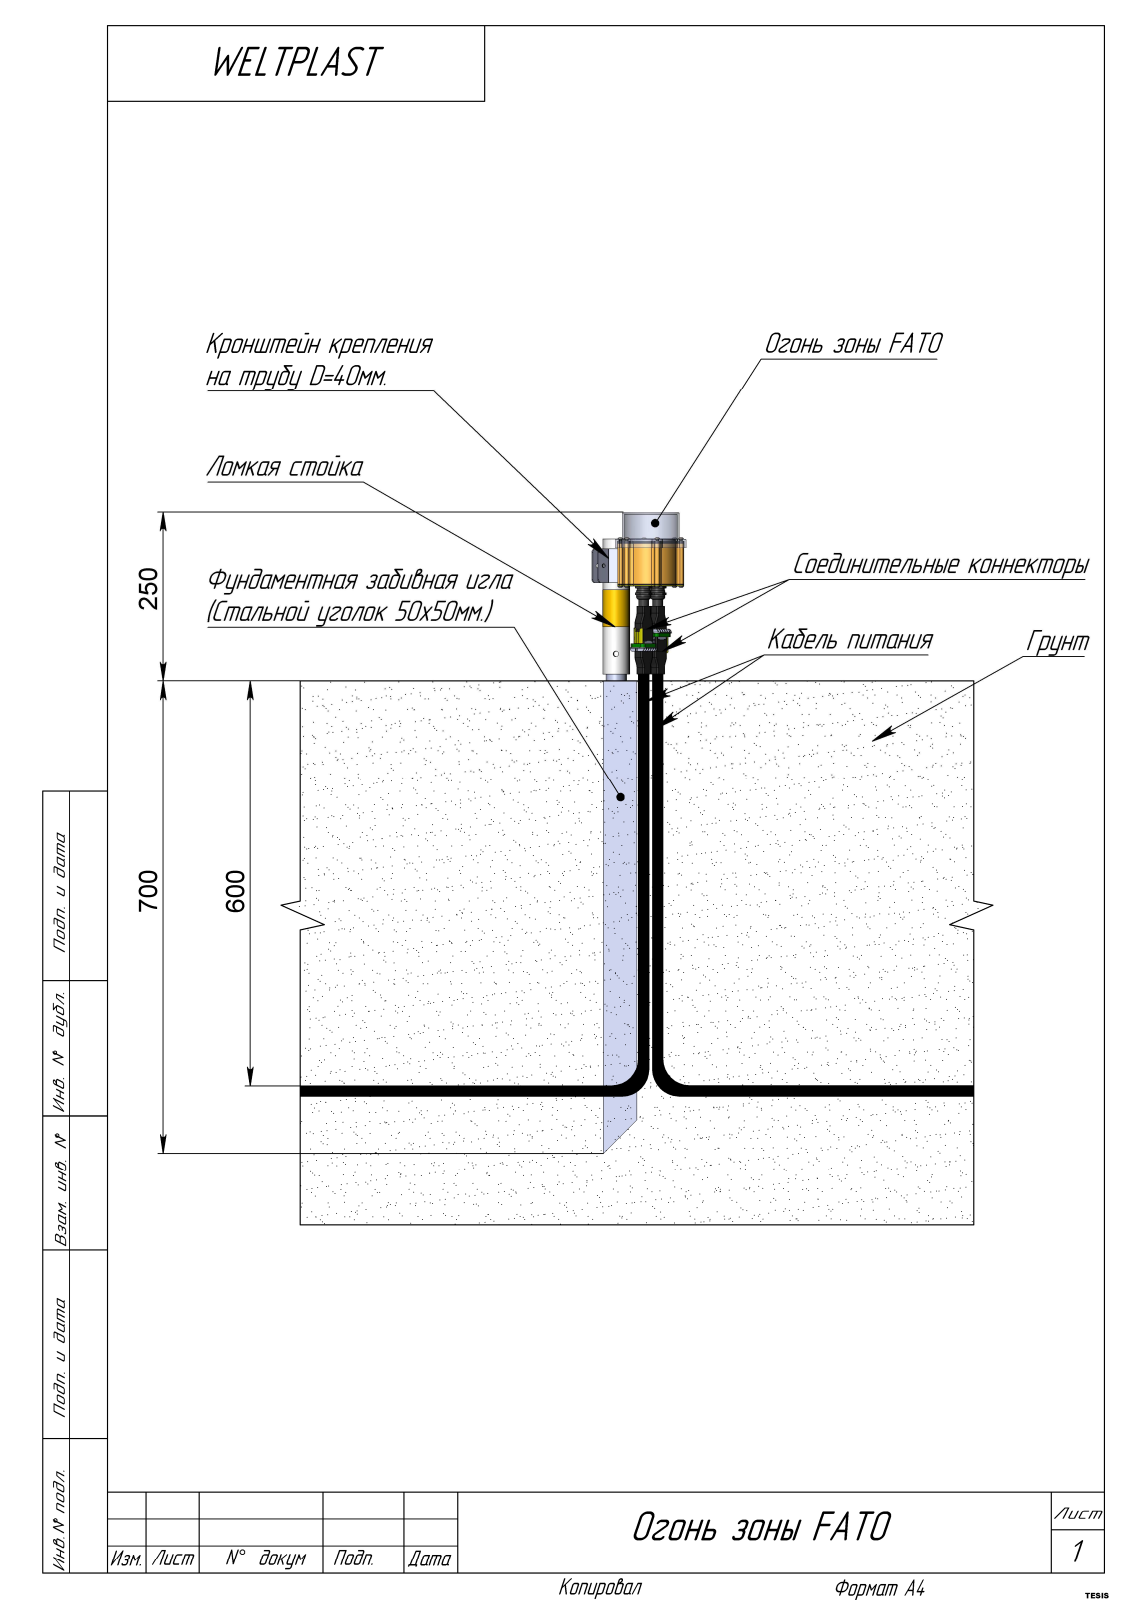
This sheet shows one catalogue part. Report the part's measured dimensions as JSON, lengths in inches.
{"part_name": "Конектор мама Сборка 1; Втулка; LLC-AB-60; гайка под провода (+8 more)", "step_written_by": "SolidWorks 2017 (AUTOMOTIVE_DESIGN)", "units": "inches", "bodies": {"solids": 44, "faces": 3008, "planar": 885, "cylindrical": 1069, "other": 1054}, "overall_size": [37.402, 5.663, 5.512], "volume_in3": 43.83, "surface_area_in2": 655.8, "round_holes": [[0.209, 8], [0.142, 6], [0.173, 6], [0.177, 6], [0.248, 6], [0.098, 3], [0.103, 3], [0.165, 2], [0.236, 2], [0.496, 2], [0.797, 2], [0.327, 1]], "round_bosses_or_shafts": [[0.299, 8], [0.157, 8], [0.846, 2], [0.776, 2], [0.591, 2], [0.413, 2], [0.236, 2], [3.346, 1]], "partial_cylinders_radius": [[0.197, 45], [0.079, 36], [0.039, 19], [0.177, 18], [0.059, 14], [0.118, 12], [0.02, 8], [0.098, 8]], "face_to_face_distances": [0.157, 0.079, 0.059, 0.118, 0.374, 0.039, 0.217, 2.52, 2.362, 1.575], "hole_center_spacings": [1.87, 3.239, 1.914, 0.114, 1.102, 2.198, 1.103, 2.197]}
